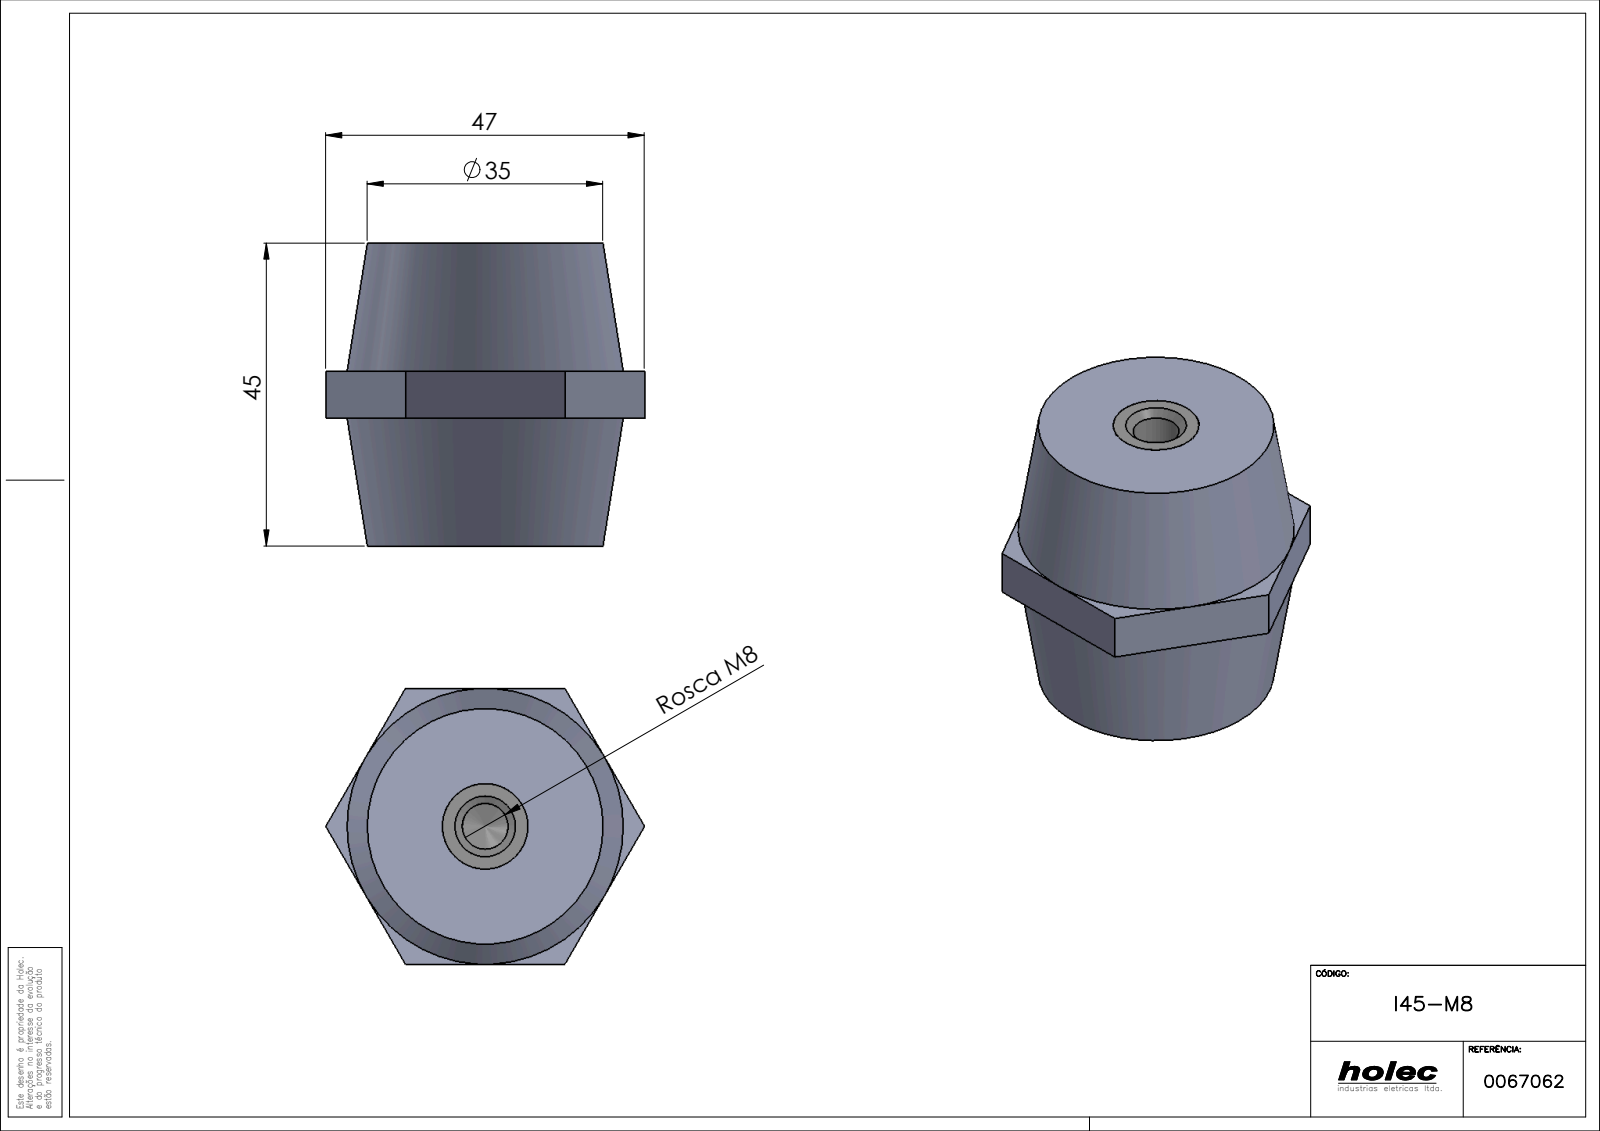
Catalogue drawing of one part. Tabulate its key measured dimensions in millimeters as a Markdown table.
| quantity | value |
| --- | --- |
| part name | I45-M8; PB1_0105(PB1_0105_08); PB1_0005 |
| STEP written by | SolidWorks 2017 (AUTOMOTIVE_DESIGN) |
| units | millimeters |
| bodies | 3 solids, 154 faces (82 planar, 12 cylindrical, 60 other) |
| overall size | 47.34 × 45 × 41 |
| volume | 52 468 mm³ |
| surface area | 11 544 mm² |
| round holes (diameter × count) | 6.8 × 1, 10 × 1 |
| main face-to-face distances | 45, 12.7, 5, 31.01, 41, 26, 14, 31, 5.01, 17.01 |
